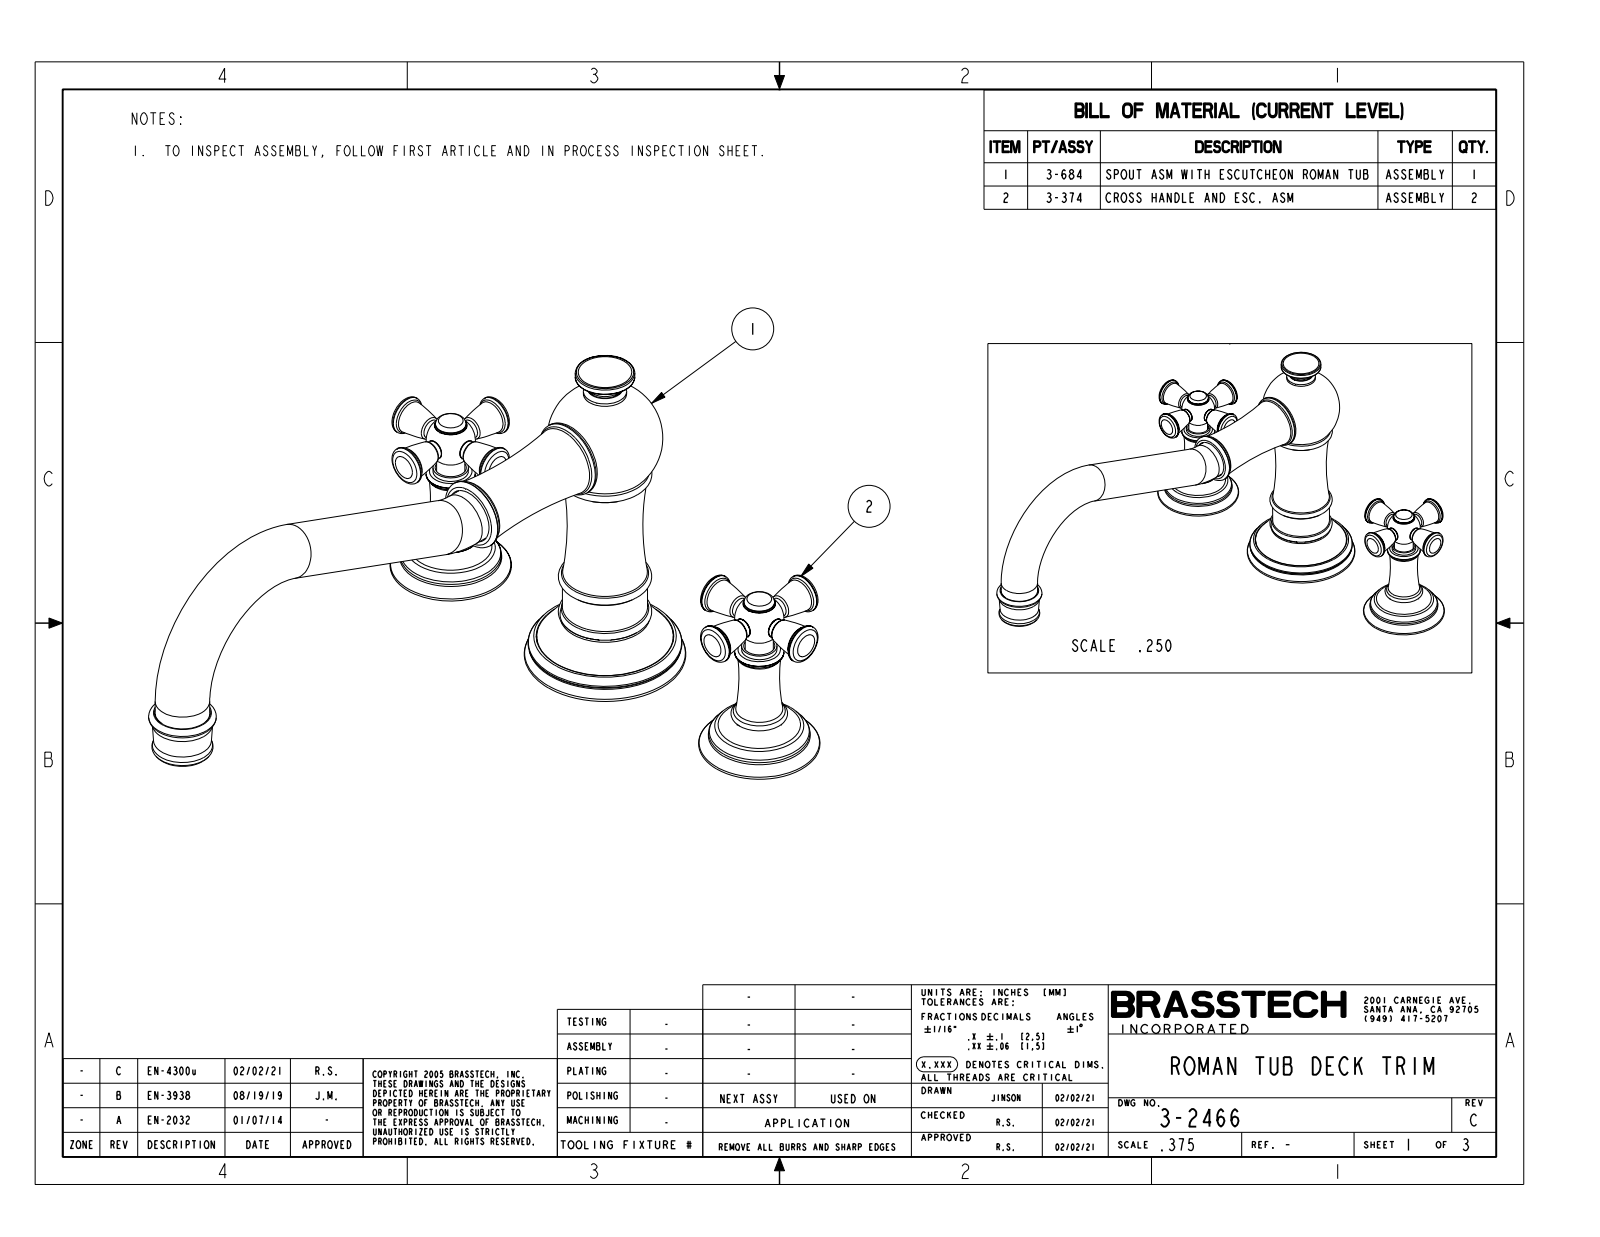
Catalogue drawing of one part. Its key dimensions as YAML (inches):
part_name: "3-2466"
step_written_by: "CREO PARAMETRIC BY PTC INC, 2018400 (CONFIG_CONTROL_DESIGN)"
units: inches
bodies: {solids: 3, faces: 370, planar: 26, cylindrical: 62, other: 282}
overall_size: [13.056, 10.528, 7.041]
volume: 33.14
surface_area: 134.4
round_bosses_or_shafts:
  - {diameter: 1, count: 3}
  - {diameter: 0.72, count: 3}
  - {diameter: 0.36, count: 3}
  - {diameter: 0.9, count: 2}
  - {diameter: 0.649, count: 2}
  - {diameter: 0.56, count: 2}
  - {diameter: 0.517, count: 2}
  - {diameter: 1.42, count: 1}
face_to_face_distances: [3.346, 2.14, 1.206, 2.22, 0.08, 1.126, 2.653, 6, 3.859, 3.78]
